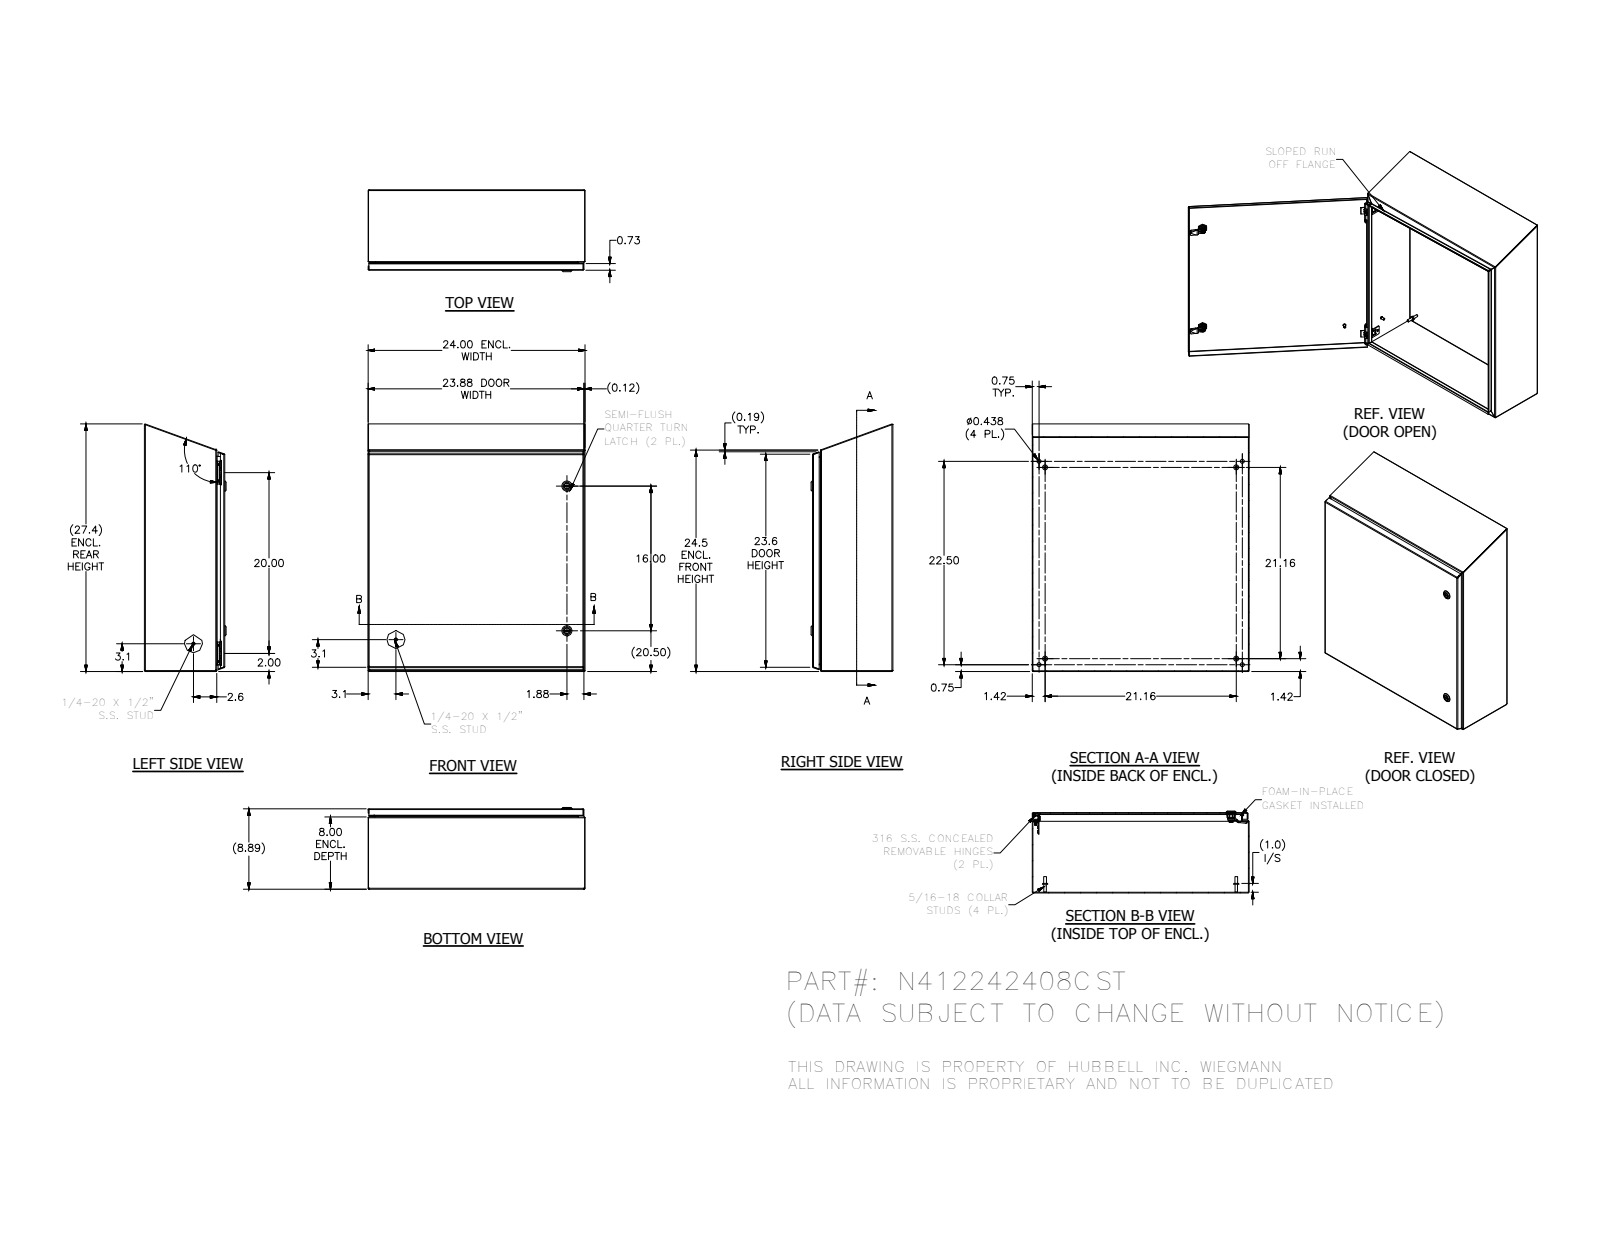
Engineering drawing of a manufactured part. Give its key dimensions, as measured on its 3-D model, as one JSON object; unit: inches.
{"part_name": "N412242408CST", "step_written_by": "SolidWorks 2018 (AUTOMOTIVE_DESIGN)", "units": "inches", "bodies": {"solids": 44, "faces": 1921, "planar": 767, "cylindrical": 690, "other": 464}, "overall_size": [27.391, 24, 9.044], "volume_in3": 167.2, "surface_area_in2": 4536, "round_holes": [[0.093, 4], [0.152, 4], [0.167, 4], [0.172, 4], [0.187, 4], [0.437, 4], [0.156, 3], [0.197, 2], [0.315, 2], [0.394, 2], [0.402, 2], [0.634, 2]], "round_bosses_or_shafts": [[0.25, 10], [0.563, 4], [0.36, 4], [0.32, 4], [0.3, 4], [0.275, 4], [0.256, 4], [0.164, 4]], "partial_cylinders_radius": [[0.012, 54], [0.031, 29], [0.05, 26], [0.02, 23], [0.105, 19], [0.016, 18], [0.125, 16], [0.032, 8]], "face_to_face_distances": [0.074, 8.813, 8.887, 8.739, 23.926, 23.852, 24, 7.926, 0.887, 0.813], "hole_center_spacings": [20, 22.5, 22.869, 0.5, 0.656, 0.66, 0.984, 1.307]}
